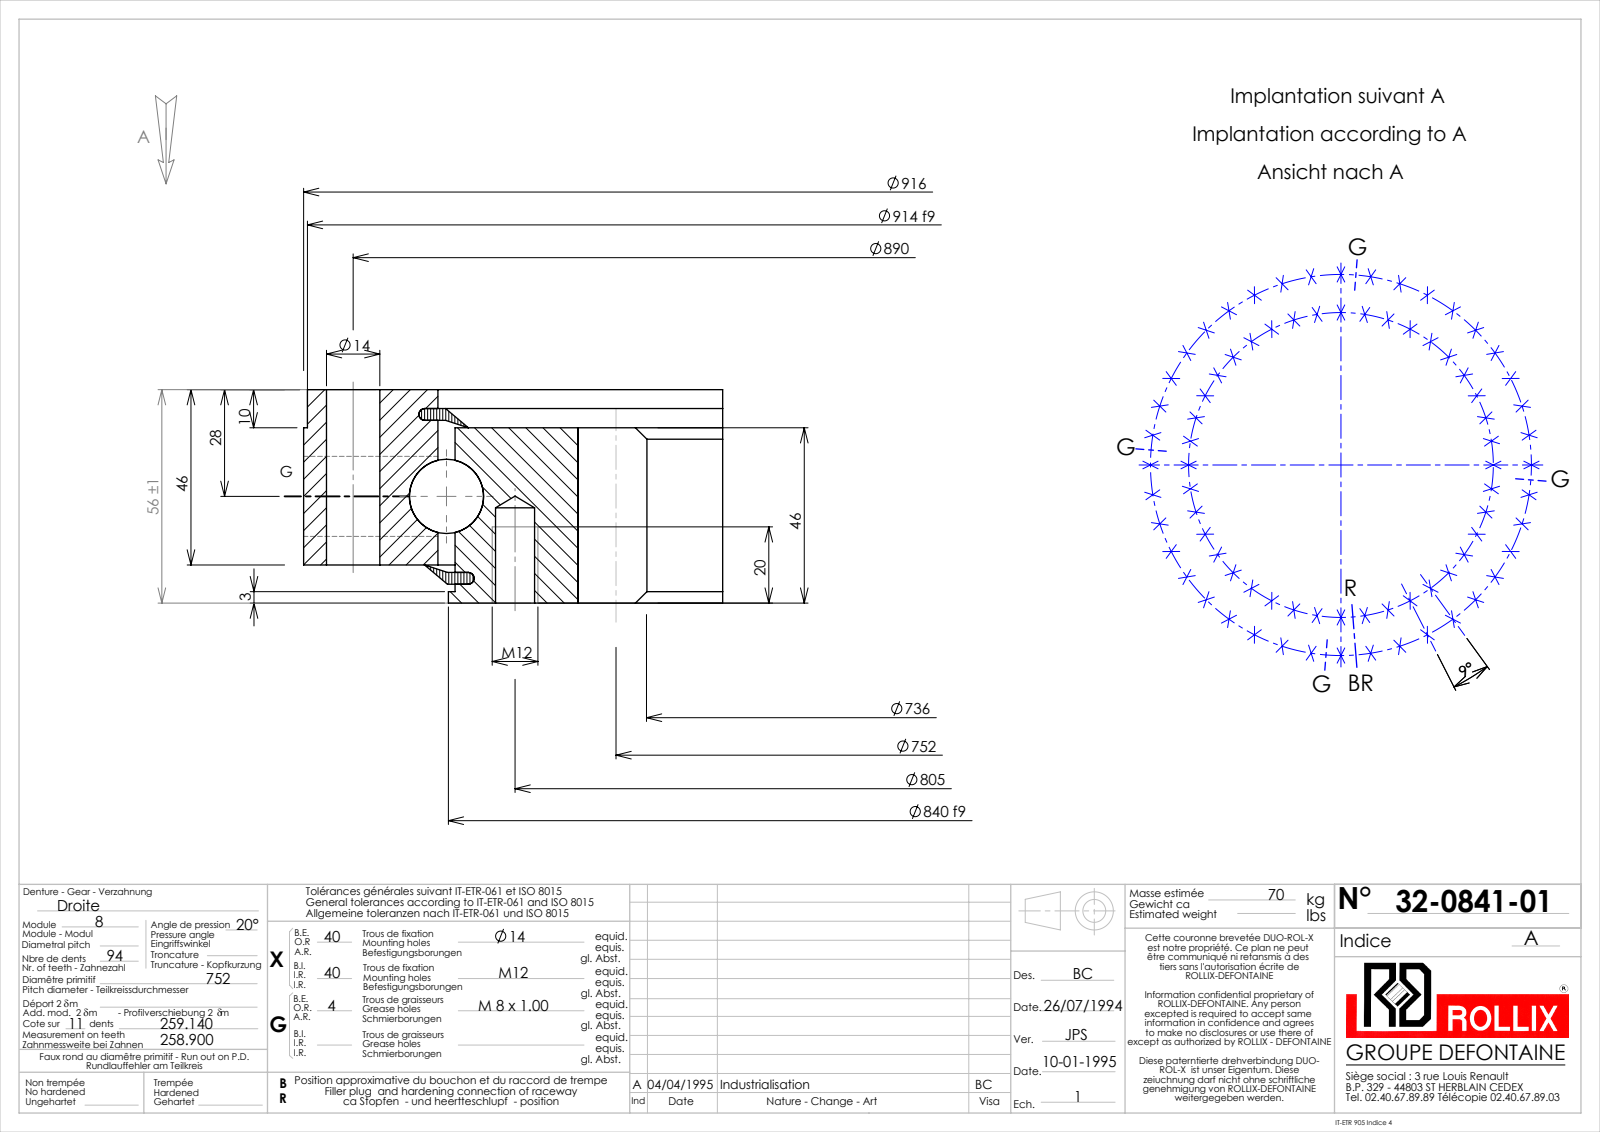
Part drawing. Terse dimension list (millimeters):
name: 32-0841-01
written by: SolidWorks 2016 (CONFIG_CONTROL_DESIGN)
unit: mm
bodies: 9 solids, 961 faces (242 planar, 383 cylindrical, 336 other)
size: 932.73 × 932.73 × 56
volume: 8 410 000 mm³; area: 1 348 000 mm²
holes: 40× ⌀10.25, 40× ⌀14, 4× ⌀7, 1× ⌀845.5
bosses: 4× ⌀8, 1× ⌀916, 1× ⌀914, 1× ⌀840, 1× ⌀836.5
rounds: 1× R368, 1× R386
face distances: 46, 10, 36, 56, 1.95, 5.05, 43, 8.05, 47.95, 37.95
hole spacings: 63.16, 365.46, 125.93, 420.61, 248.76, 187.92, 308.06, 651.26
